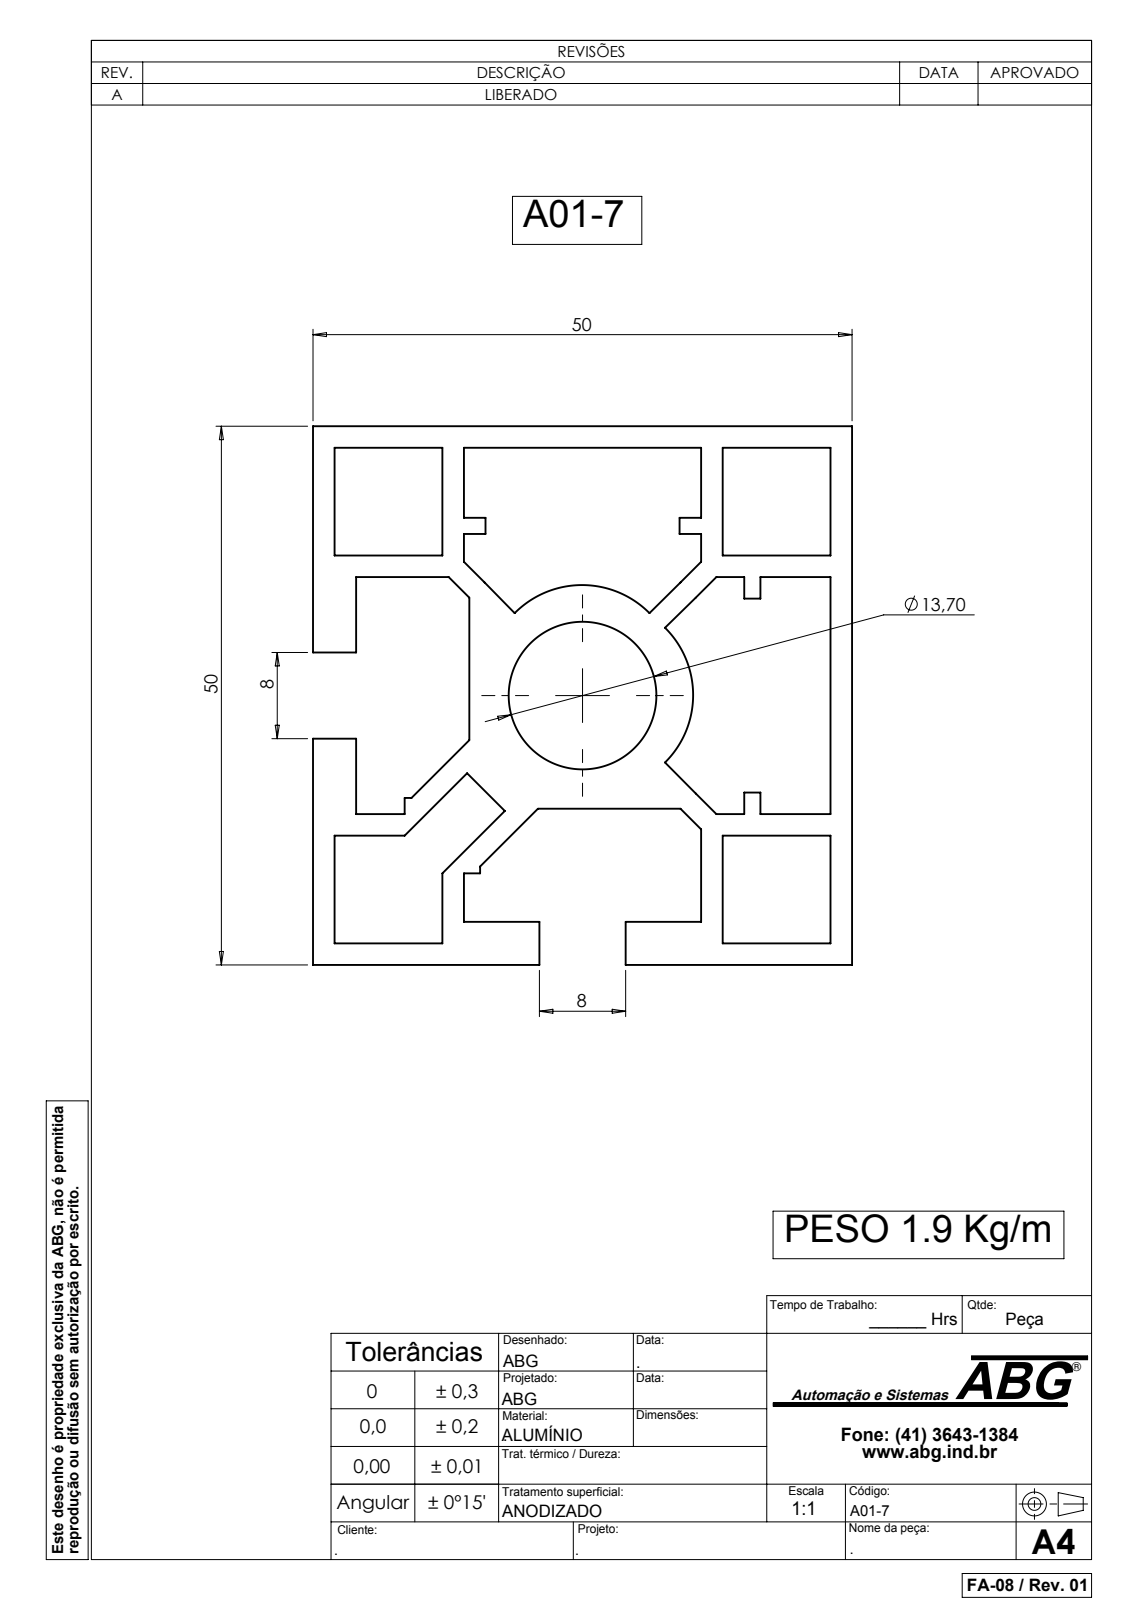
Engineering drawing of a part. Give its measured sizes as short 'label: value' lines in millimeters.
name: A01-7
written by: SolidWorks 2007 (CONFIG_CONTROL_DESIGN)
unit: mm
bodies: 1 solid, 84 faces (79 planar, 5 cylindrical, 0 other)
size: 6000 × 50 × 50
volume: 5 217 000 mm³; area: 4 081 000 mm²
holes: 1× ⌀13.7
rounds: 2× R8.8
face distances: 2, 36, 12, 48, 10, 34, 50, 38, 14, 46
